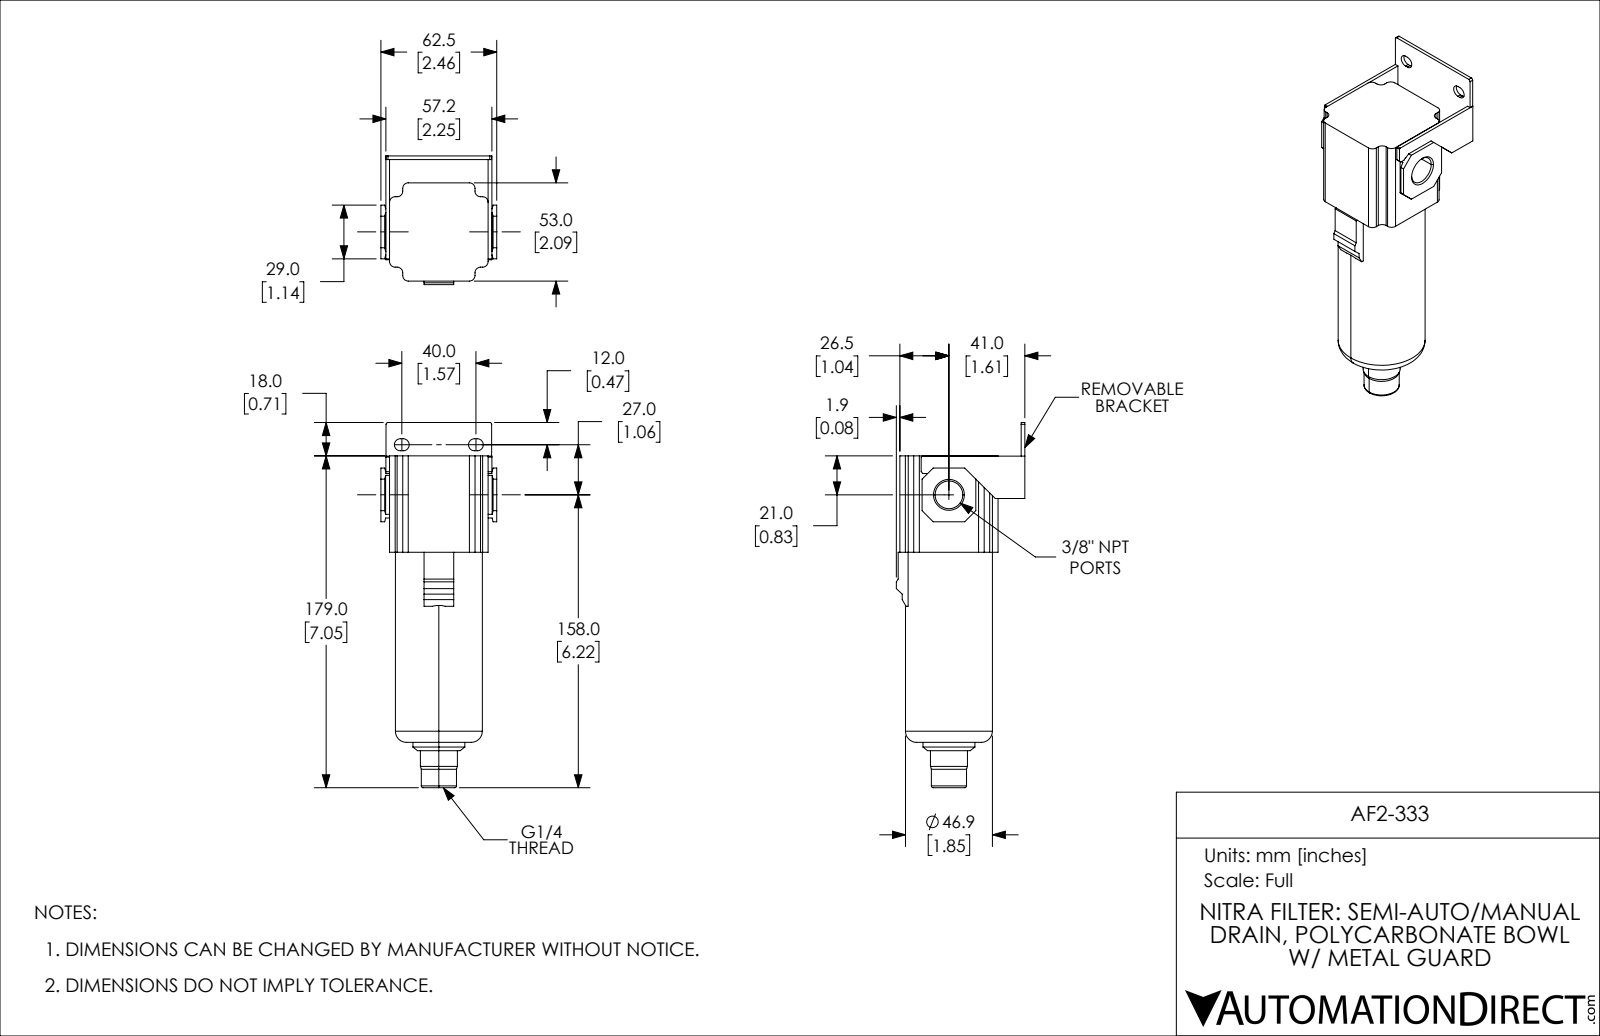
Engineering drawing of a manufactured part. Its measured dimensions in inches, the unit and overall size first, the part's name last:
Units: inches
Overall size (bounding box): 7.756 × 2.733 × 2.461
Round holes (diameter × count): ⌀0.337 ×1, ⌀0.589 ×1
Round bosses / shafts (diameter × count): ⌀1.846 ×1, ⌀1.102 ×1, ⌀0.787 ×1, ⌀0.748 ×1
Partial cylindrical surfaces — rounded edges, fillets, slot ends (radius × count): R0.118 ×12, R0.128 ×4, R0.039 ×2
Main face-to-face distances: 0.079, 0.492, 0.571, 2.657, 2.579, 2.087, 2.173, 2.094, 0.104, 0.183
Volume: 20.09 in³ · Surface area: 65.35 in²
Bodies: 1 solid, 137 faces (91 planar, 32 cylindrical, 14 other)
Part name (STEP PRODUCT): AF2-333
STEP written by: SolidWorks 2019 (CONFIG_CONTROL_DESIGN)
